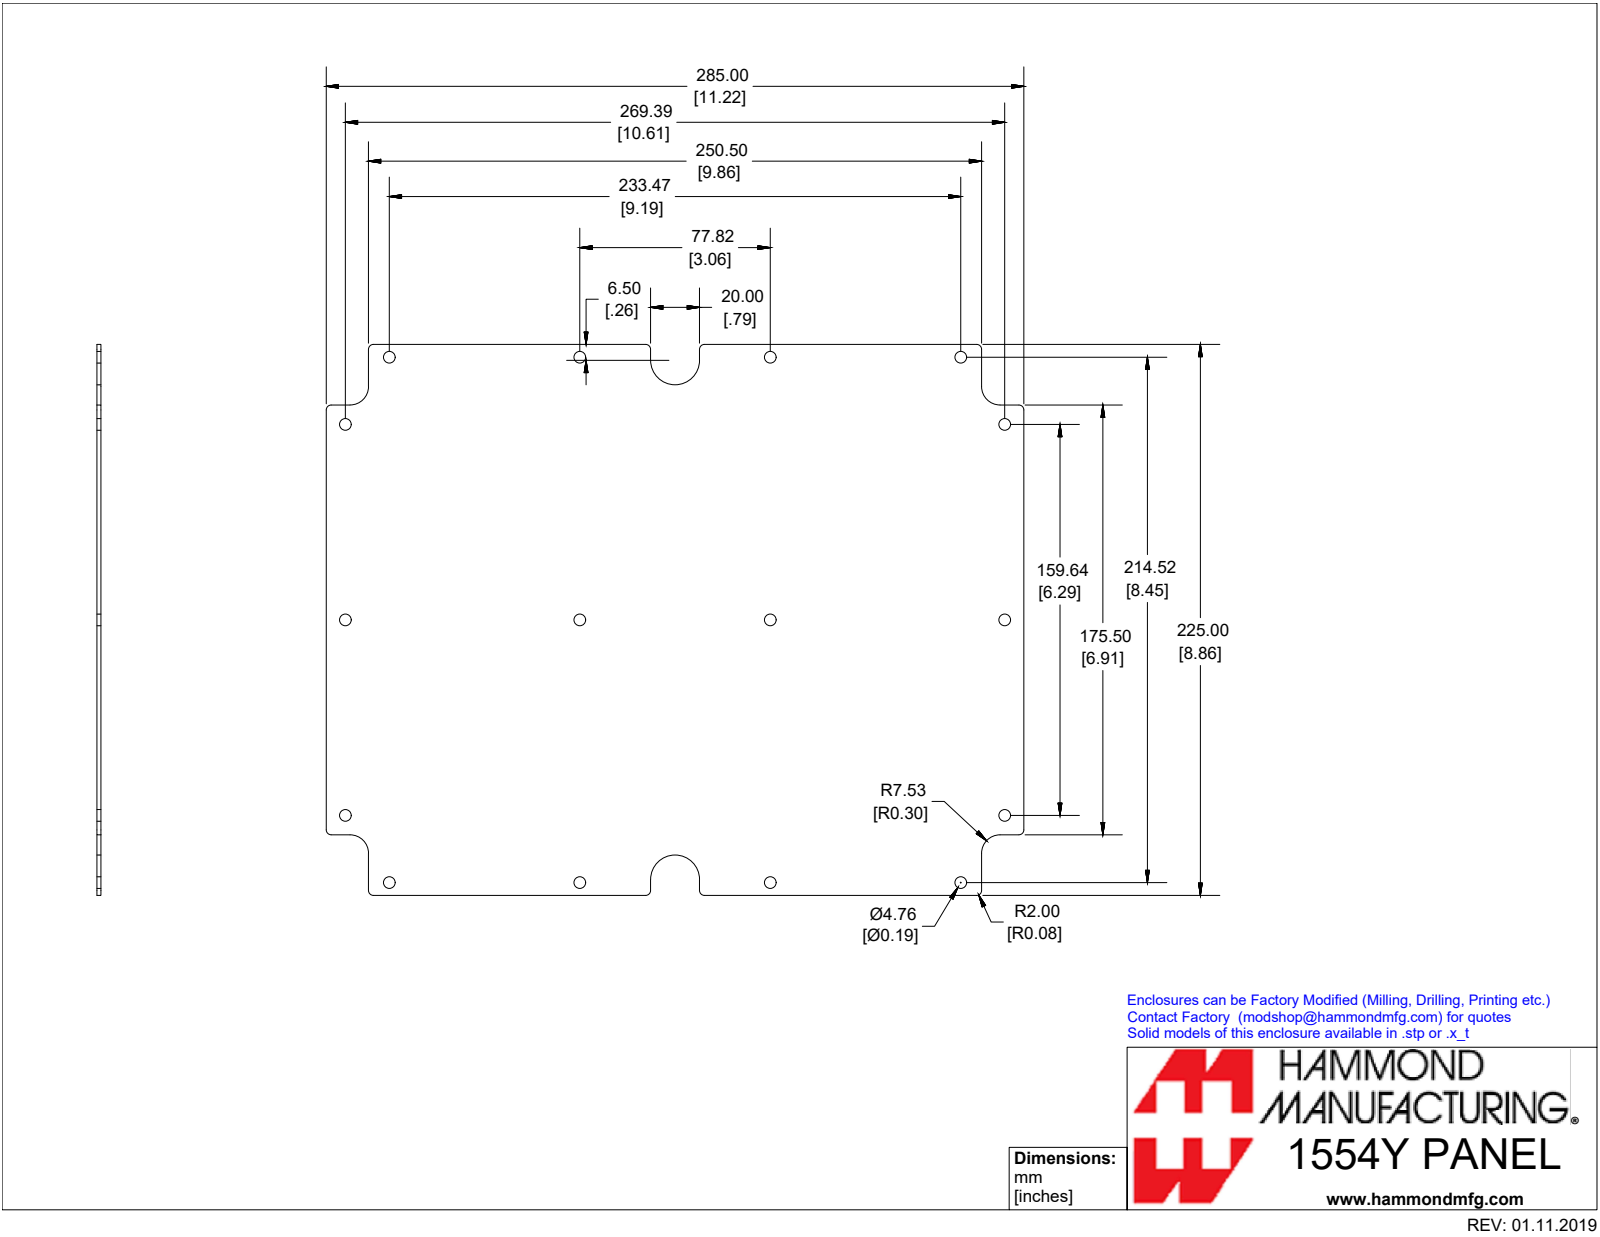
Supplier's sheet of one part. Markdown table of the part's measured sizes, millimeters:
| quantity | value |
| --- | --- |
| part name | 1554YPL |
| STEP written by | SolidWorks 2019 (CONFIG_CONTROL_DESIGN) |
| units | millimeters |
| bodies | 1 solid, 54 faces (20 planar, 34 cylindrical, 0 other) |
| overall size | 285 × 225 × 1.6 |
| volume | 100 100 mm³ |
| surface area | 125 300 mm² |
| round holes (diameter × count) | 4.7 × 16 |
| partial cylindrical surfaces (radius × count) | 2 × 12, 7.5 × 4, 10 × 2 |
| main face-to-face distances | 1.6, 225, 285, 17.2, 267.7, 24.7, 200.3, 250.5, 132.5, 152.5 |
| hole center spacings | 132.5, 77.8, 228.2, 32.8, 79.8, 99.6, 107.3, 108.7 |
